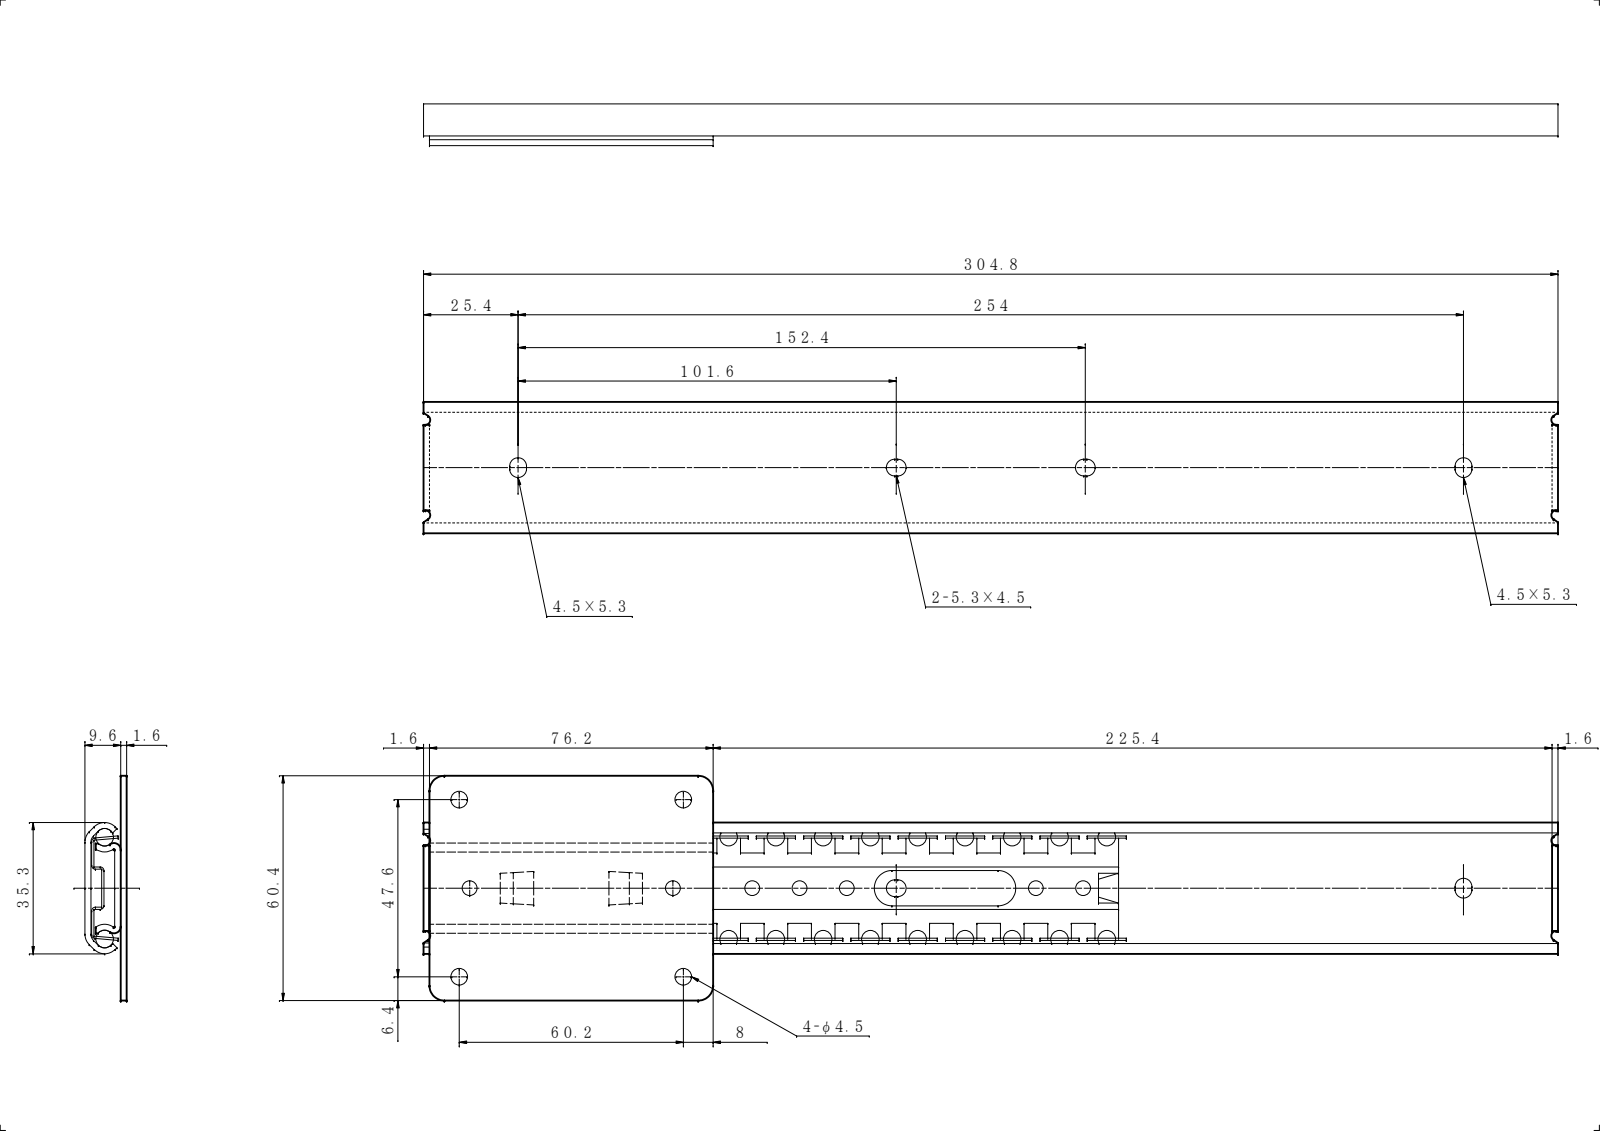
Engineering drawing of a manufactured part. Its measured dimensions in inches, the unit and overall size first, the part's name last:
Units: inches
Overall size (bounding box): 12 × 2.378 × 0.441
Round holes (diameter × count): ⌀0.177 ×4, ⌀0.165 ×2
Partial cylindrical surfaces — rounded edges, fillets, slot ends (radius × count): R0.089 ×8, R0.118 ×6, R0.157 ×6, R0.008 ×2, R0.071 ×2, R0.079 ×2, R0.094 ×2, R0.094 ×2
Main face-to-face distances: 0.063, 0.378, 0.315, 0.441, 0.252, 0.126, 0.184, 0.121, 1.011, 1.074
Hole centre spacings: 0.95, 2.692, 1.874, 2.37, 3.022, 2.677
Volume: 2.048 in³ · Surface area: 63.58 in²
Bodies: 2 solids, 98 faces (44 planar, 54 cylindrical, 0 other)
Part name (STEP PRODUCT): IM #3; OM-3511-12; 3511-12#3
STEP written by: SolidWorks 2019 (CONFIG_CONTROL_DESIGN)
